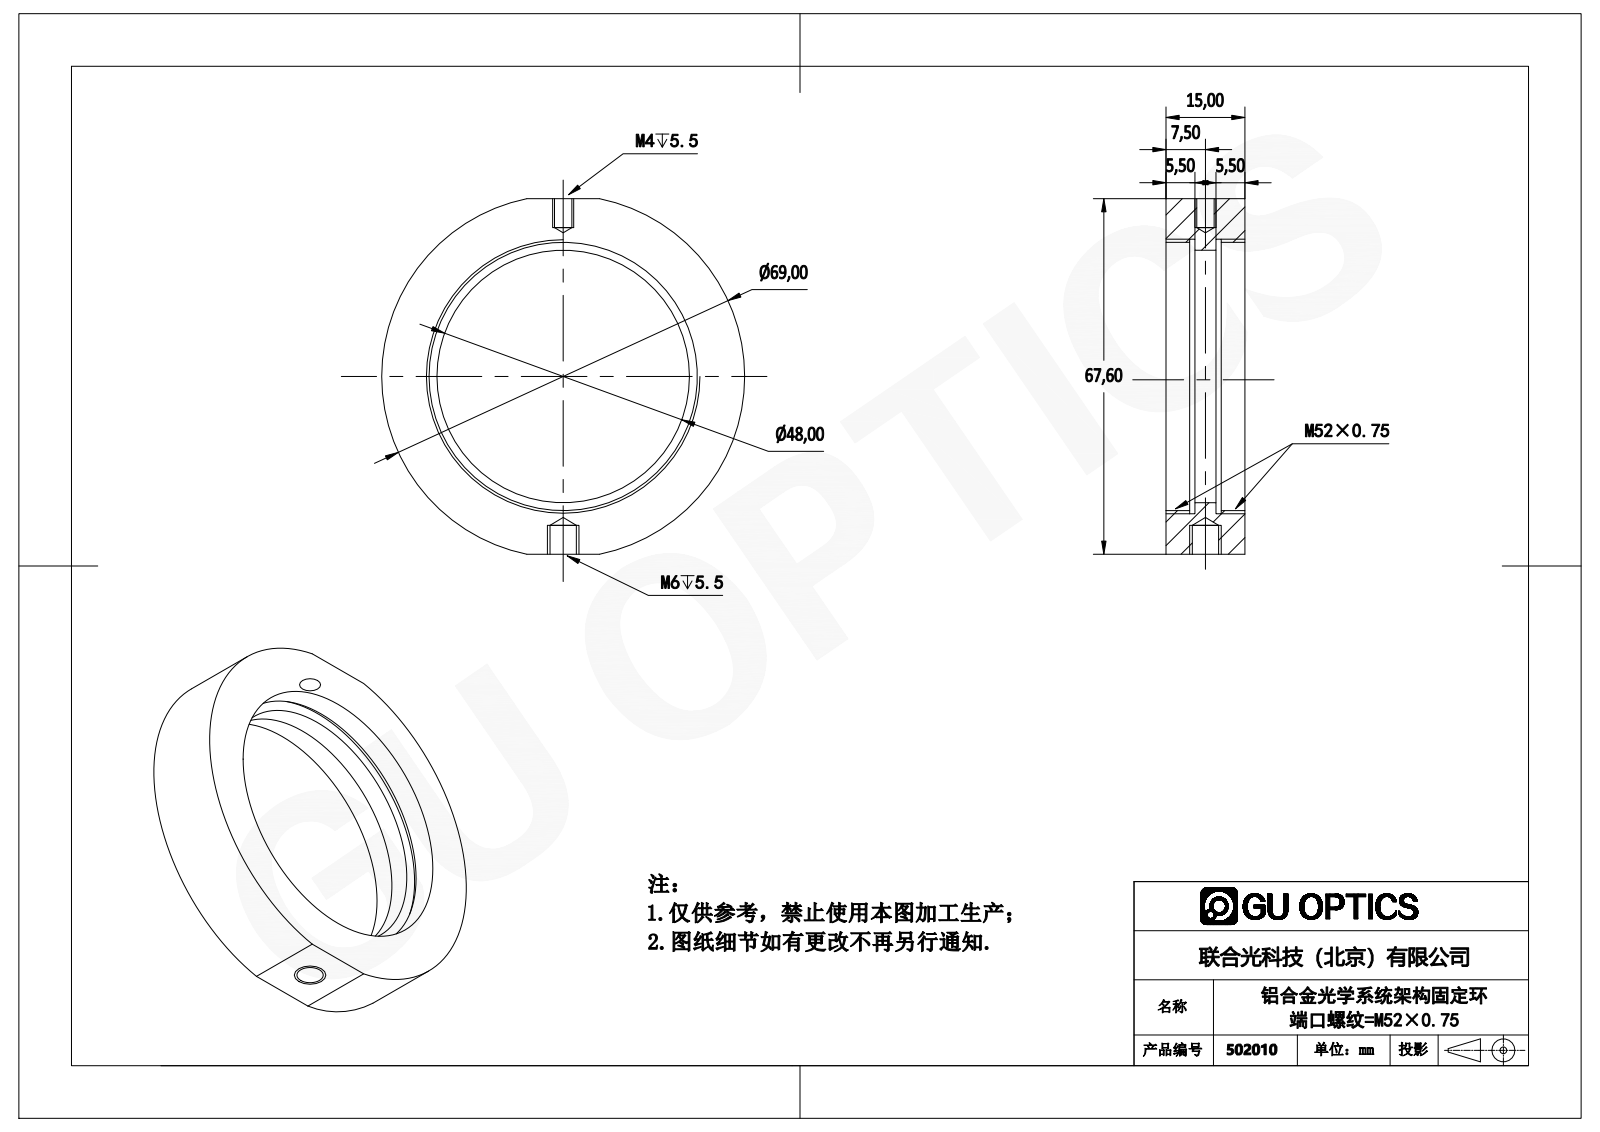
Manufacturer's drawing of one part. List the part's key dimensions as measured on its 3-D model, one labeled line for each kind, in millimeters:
Part name (STEP PRODUCT): 502010
STEP written by: SolidWorks 2016 (CONFIG_CONTROL_DESIGN)
Units: millimetres
Bodies: 1 solid, 29 faces (8 planar, 17 cylindrical, 4 other)
Overall size (bounding box): 69 × 67.6 × 15
Volume: 25 824 mm³ · Surface area: 9 993 mm²
Round holes (diameter × count): ⌀3.3 ×1, ⌀5 ×1, ⌀48 ×1, ⌀51 ×1, ⌀52.2 ×1
Round bosses / shafts (diameter × count): ⌀69 ×1
Main face-to-face distances: 15, 5.5, 9.5, 4, 4.5, 10.5, 1, 5, 67.6, 6
